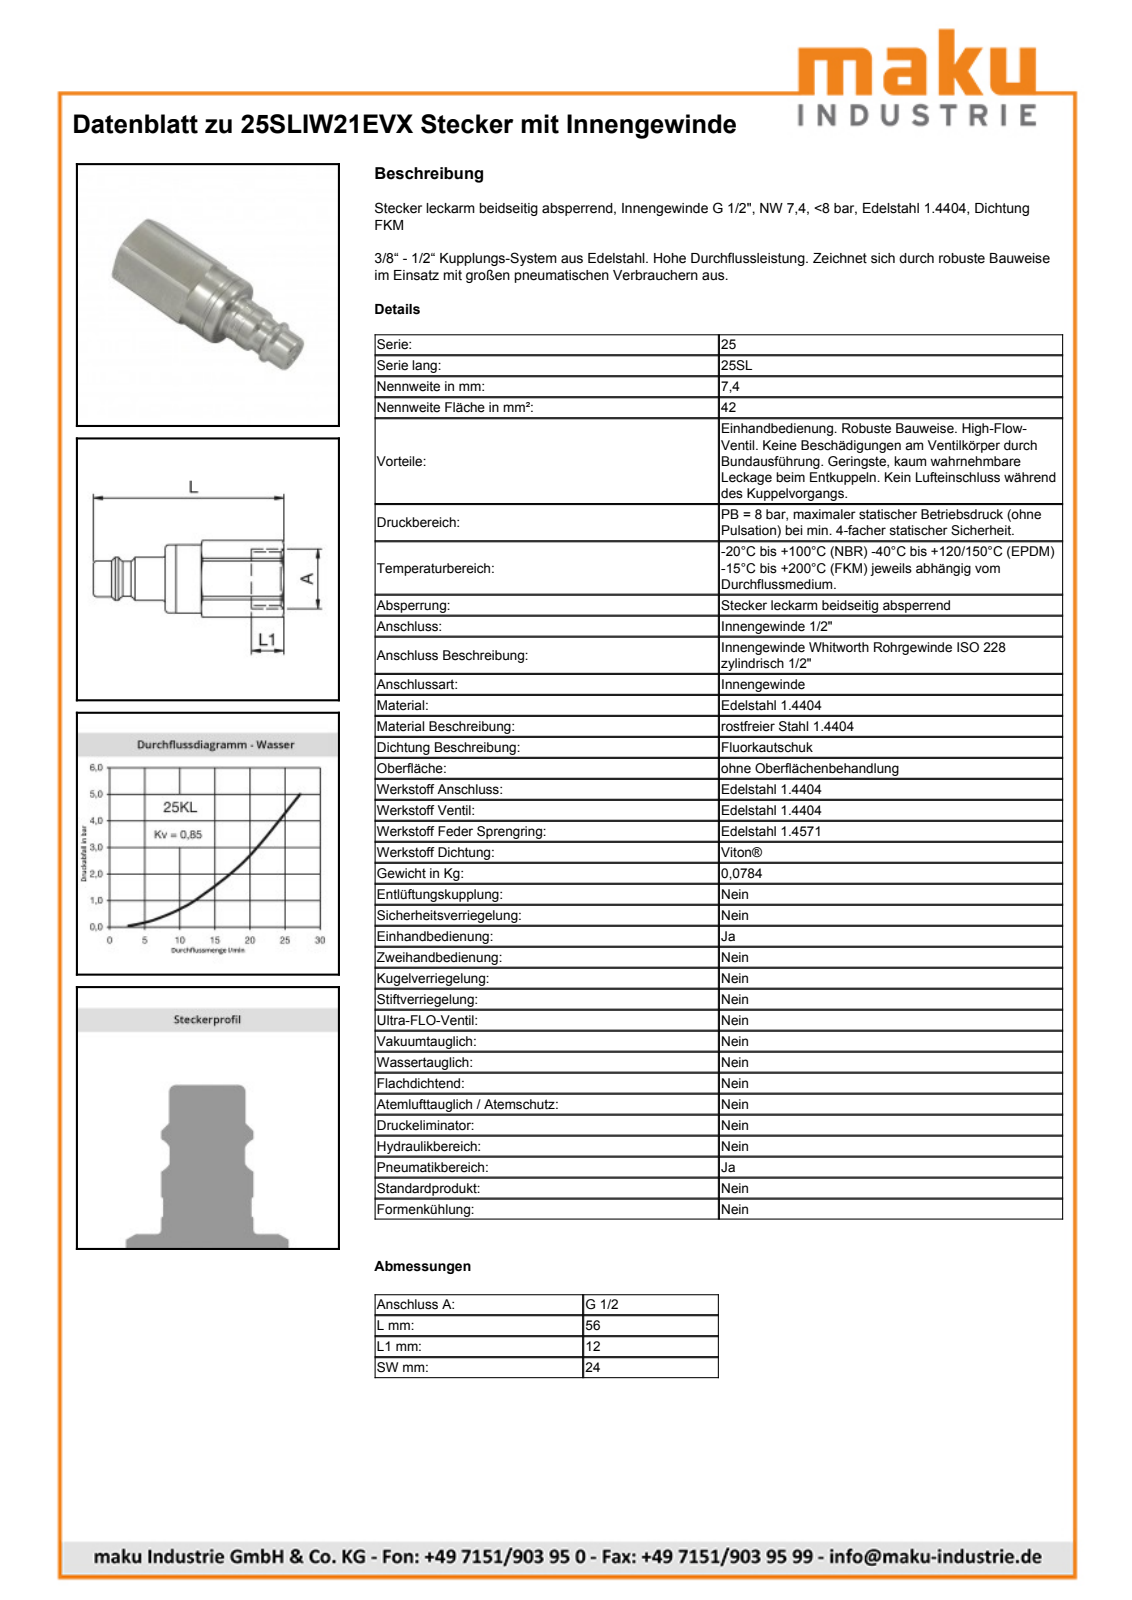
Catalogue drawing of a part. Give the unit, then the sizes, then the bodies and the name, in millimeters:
Units: millimetres
Overall size (bounding box): 56 × 26.96 × 25.39
Round holes (diameter × count): ⌀7.85 ×1, ⌀8.6 ×1, ⌀9.5 ×1, ⌀14 ×1, ⌀15.1 ×1, ⌀16 ×1, ⌀18.63 ×1
Round bosses / shafts (diameter × count): ⌀19 ×1, ⌀18.95 ×1, ⌀14.5 ×1, ⌀12 ×1, ⌀9.9 ×1, ⌀9.75 ×1, ⌀7.77 ×1
Partial cylindrical surfaces — rounded edges, fillets, slot ends (radius × count): R13.53 ×1
Main face-to-face distances: 24, 24.02, 14.05, 26.05, 12, 9.95, 36, 20, 29.95, 44
Volume: 12 054 mm³ · Surface area: 7 754 mm²
Bodies: 1 solid, 66 faces (16 planar, 22 cylindrical, 28 other)
Part name (STEP PRODUCT): D110448
STEP written by: Autodesk Inventor 2013 (AUTOMOTIVE_DESIGN)
